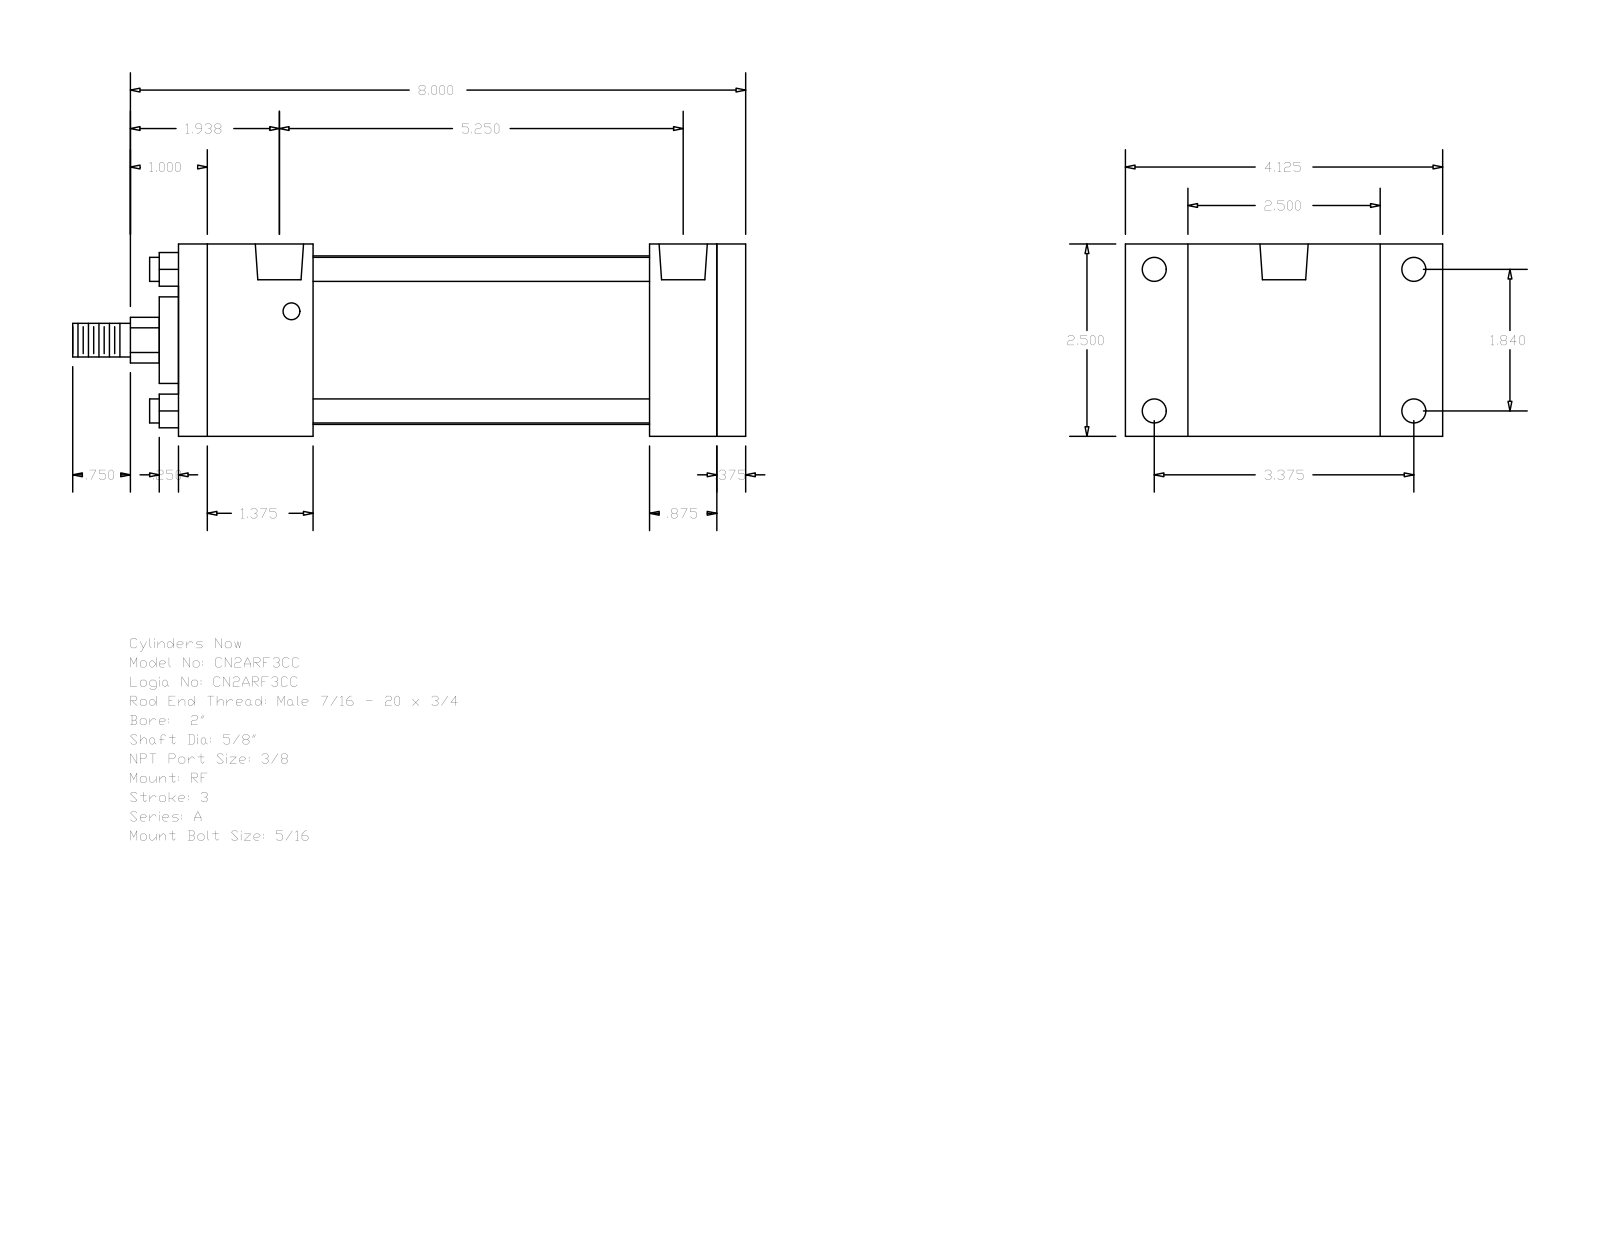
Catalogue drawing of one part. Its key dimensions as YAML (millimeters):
part_name: "A_RF__0200_0.625"
step_written_by: "GSSL Pune (CONFIG_CONTROL_DESIGN)"
units: millimeters
bodies: {solids: 0, faces: 92, planar: 64, cylindrical: 28, other: 0}
overall_size: [222.25, 104.78, 63.5]
round_holes:
  - {diameter: 5.56, count: 4}
  - {diameter: 7.94, count: 4}
  - {diameter: 15.93, count: 2}
round_bosses_or_shafts:
  - {diameter: 7.94, count: 4}
  - {diameter: 55.63, count: 1}
  - {diameter: 28.57, count: 1}
  - {diameter: 15.88, count: 1}
  - {diameter: 11.11, count: 1}
partial_cylinders:
  - {radius: 7.54, count: 1}
face_to_face_distances: [63.5, 187.32, 177.8, 9.52, 44.45, 133.35, 142.87, 155.57, 111.12, 22.23]
hole_center_spacings: [46.74, 85.72, 97.63, 125.4, 3.97, 3.98, 129.37, 129.38]
